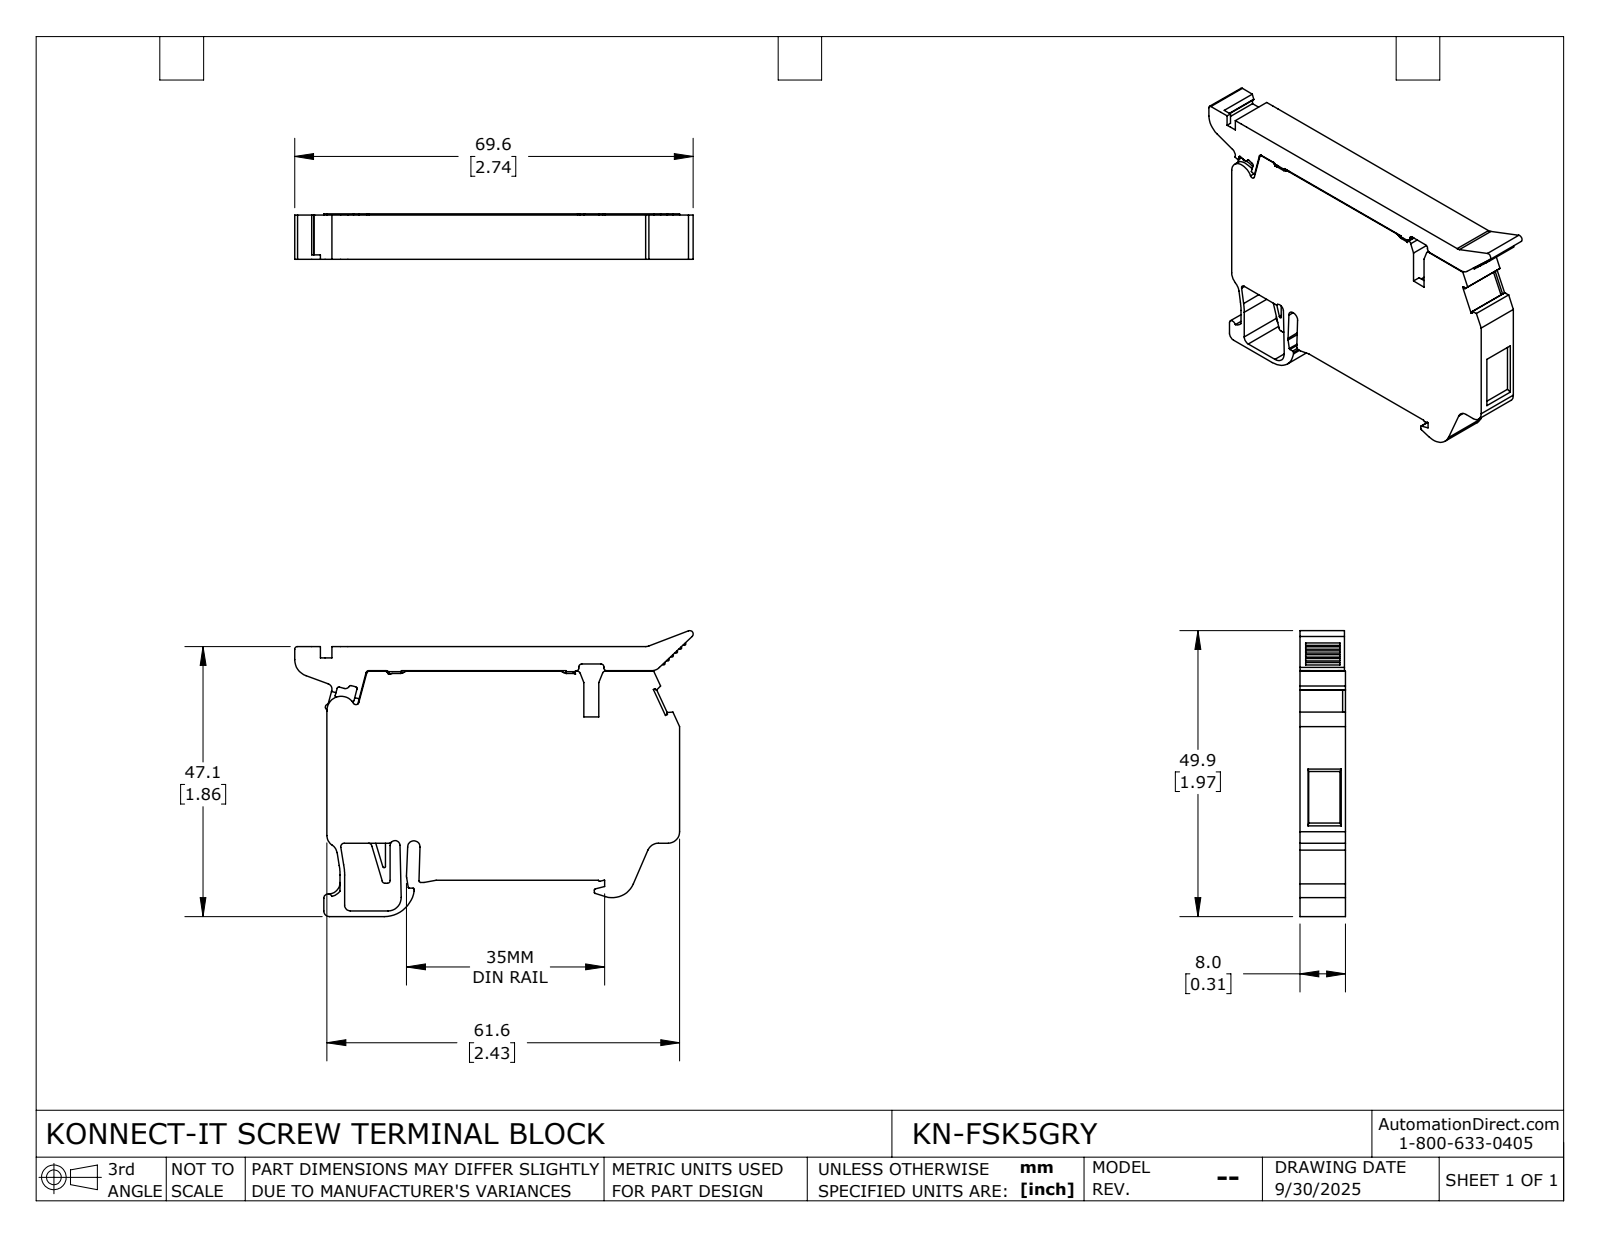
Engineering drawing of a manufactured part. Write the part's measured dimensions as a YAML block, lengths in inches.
part_name: "KN-FSK5GRY"
step_written_by: "SolidWorks 2024 (CONFIG_CONTROL_DESIGN)"
units: inches
bodies: {solids: 1, faces: 318, planar: 181, cylindrical: 124, other: 13}
overall_size: [2.74, 1.965, 0.313]
volume: 1.146
surface_area: 13.11
round_holes:
  - {diameter: 0.197, count: 1}
partial_cylinders:
  - {radius: 0.02, count: 16}
  - {radius: 0.039, count: 10}
  - {radius: 0.012, count: 8}
  - {radius: 0.079, count: 8}
  - {radius: 0.008, count: 7}
  - {radius: 0.01, count: 7}
  - {radius: 0.004, count: 4}
  - {radius: 0.098, count: 3}
face_to_face_distances: [0.313, 0.305, 0.165, 0.024, 0.02, 1.44, 1.606, 0.189, 1.417, 2.406]
